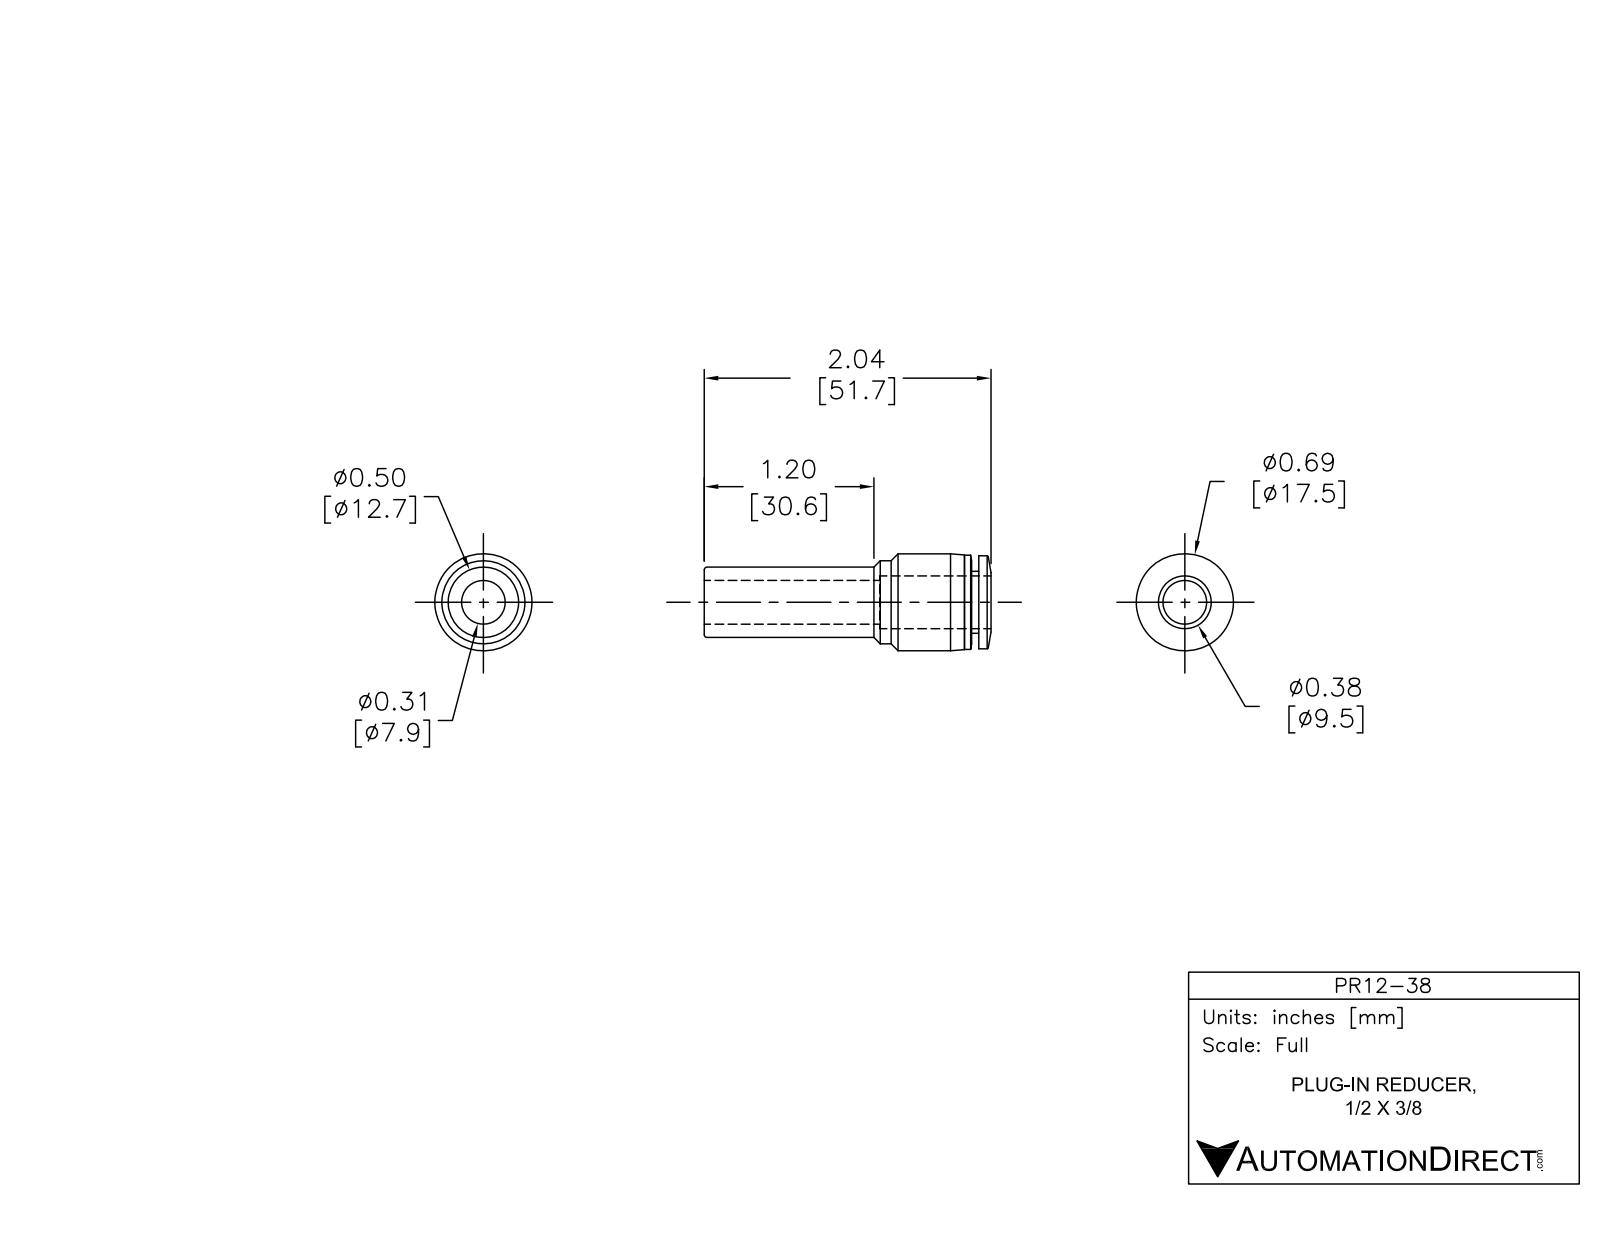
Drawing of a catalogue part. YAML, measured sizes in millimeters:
part_name: "PR12-38"
step_written_by: "SolidWorks 2015 (AUTOMOTIVE_DESIGN)"
units: millimeters
bodies: {solids: 1, faces: 39, planar: 5, cylindrical: 16, other: 18}
overall_size: [51.8, 17.5, 17.5]
volume: 5290
surface_area: 4230
round_holes:
  - {diameter: 8, count: 1}
  - {diameter: 9.8, count: 1}
round_bosses_or_shafts:
  - {diameter: 17.5, count: 1}
  - {diameter: 17, count: 1}
  - {diameter: 16.8, count: 1}
  - {diameter: 15, count: 1}
  - {diameter: 12.7, count: 1}
  - {diameter: 11.2, count: 1}
face_to_face_distances: [1.3, 48.3, 49.6, 31.7, 16.6, 17.9, 47, 15.3, 2.6]
